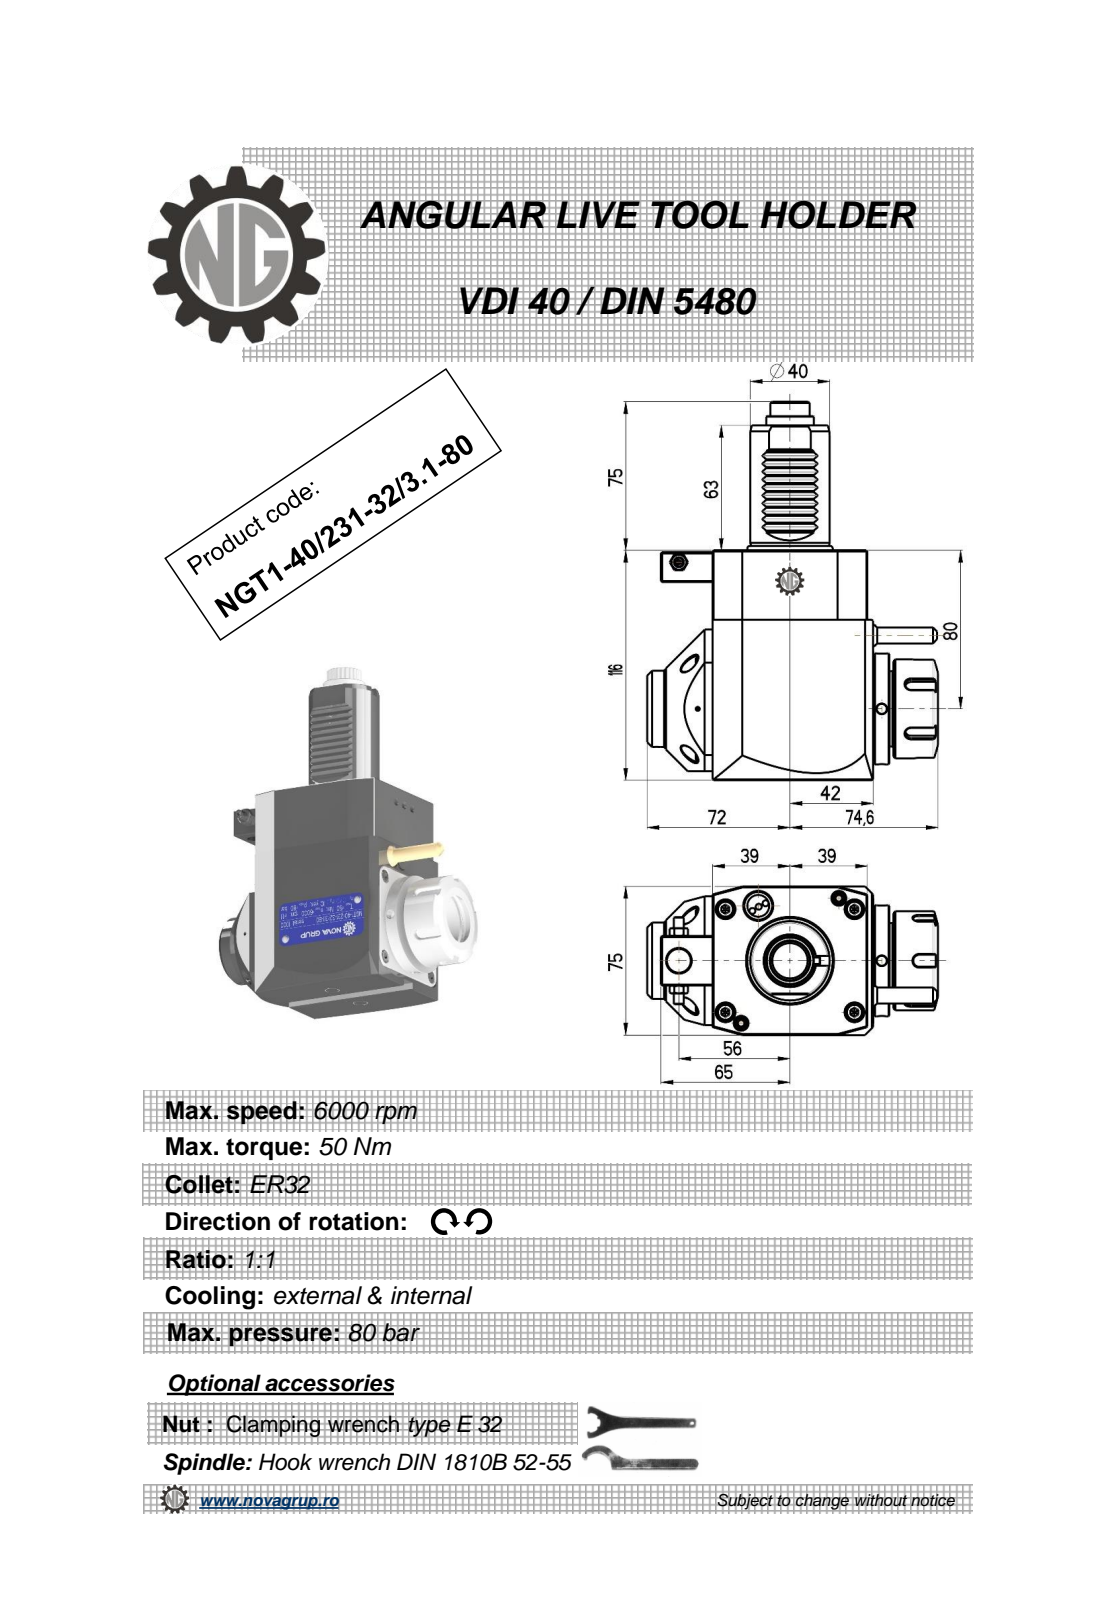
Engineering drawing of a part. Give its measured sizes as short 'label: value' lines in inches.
name: NGT1_40_231_32_3_1_80
written by: PRO/ENGINEER BY PARAMETRIC TECHNOLOGY CORPORATION, 2010280 (CONFIG_CONTROL_DESIGN)
unit: in
bodies: 1 solid, 537 faces (193 planar, 183 cylindrical, 161 other)
size: 7.52 × 5.772 × 2.953
volume: 55.75 in³; area: 113.3 in²
holes: 3× ⌀0.197, 1× ⌀0.118, 1× ⌀0.165, 1× ⌀0.374, 1× ⌀0.472, 1× ⌀1.063
bosses: 1× ⌀2.205, 1× ⌀1.969, 1× ⌀1.693, 1× ⌀1.575, 1× ⌀1.516, 1× ⌀0.945, 1× ⌀0.441, 1× ⌀0.353
rounds: 48× R0.082, 12× R0.01, 10× R0.012, 6× R0.009, 5× R0.118, 1× R0.357, 1× R0.391, 1× R0.591
face distances: 2.953, 4.567, 3.189, 3.071, 0.118, 0.295, 3.181, 0.11, 0.02, 4.37
hole spacings: 1.523, 1.611, 2.815, 4.026, 4.969
